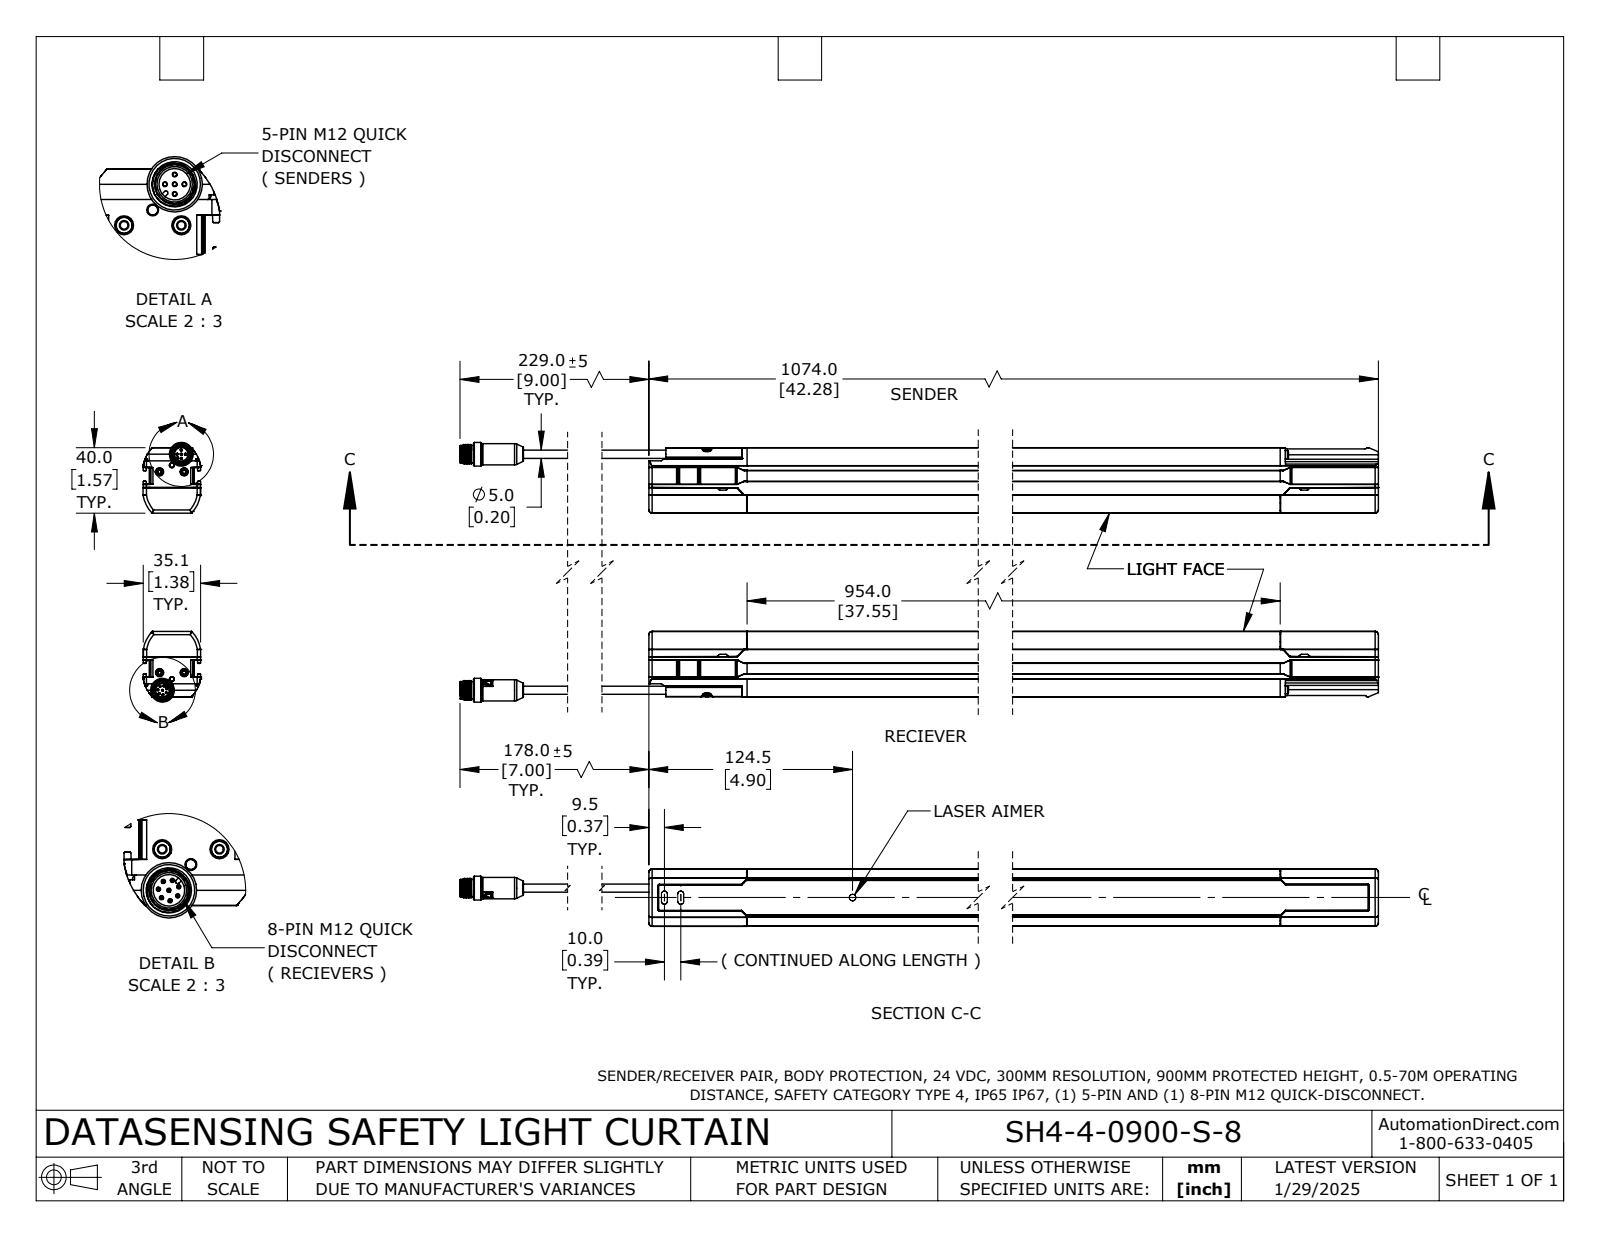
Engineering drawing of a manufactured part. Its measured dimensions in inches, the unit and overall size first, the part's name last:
Units: inches
Overall size (bounding box): 51.272 × 6.248 × 1.384
Round holes (diameter × count): ⌀0.197 ×5, ⌀0.079 ×4, ⌀0.118 ×4, ⌀0.079 ×2, ⌀0.325 ×2, ⌀0.382 ×2, ⌀0.407 ×2, ⌀0.425 ×2, ⌀0.11 ×1, ⌀0.138 ×1
Round bosses / shafts (diameter × count): ⌀0.197 ×10, ⌀0.087 ×8, ⌀0.031 ×8, ⌀0.039 ×5, ⌀0.172 ×4, ⌀0.571 ×2, ⌀0.512 ×2, ⌀0.417 ×2
Partial cylindrical surfaces — rounded edges, fillets, slot ends (radius × count): R0.01 ×164, R0.016 ×66, R0.02 ×50, R0.008 ×36, R0.031 ×20, R0.031 ×12, R0.079 ×12, R0.059 ×10
Main face-to-face distances: 1.496, 4.496, 0.156, 1.222, 3, 1.378, 5.992, 1.067, 4.634, 1.033
Hole centre spacings: 0.429, 0.591, 0.672, 4.831, 4.867, 5.254, 5.28, 5.695
Volume: 154.3 in³ · Surface area: 681.7 in²
Bodies: 5 solids, 2644 faces (1206 planar, 786 cylindrical, 652 other)
Part name (STEP PRODUCT): SH4-4-0900-S-8
STEP written by: SolidWorks 2024 (AUTOMOTIVE_DESIGN)
